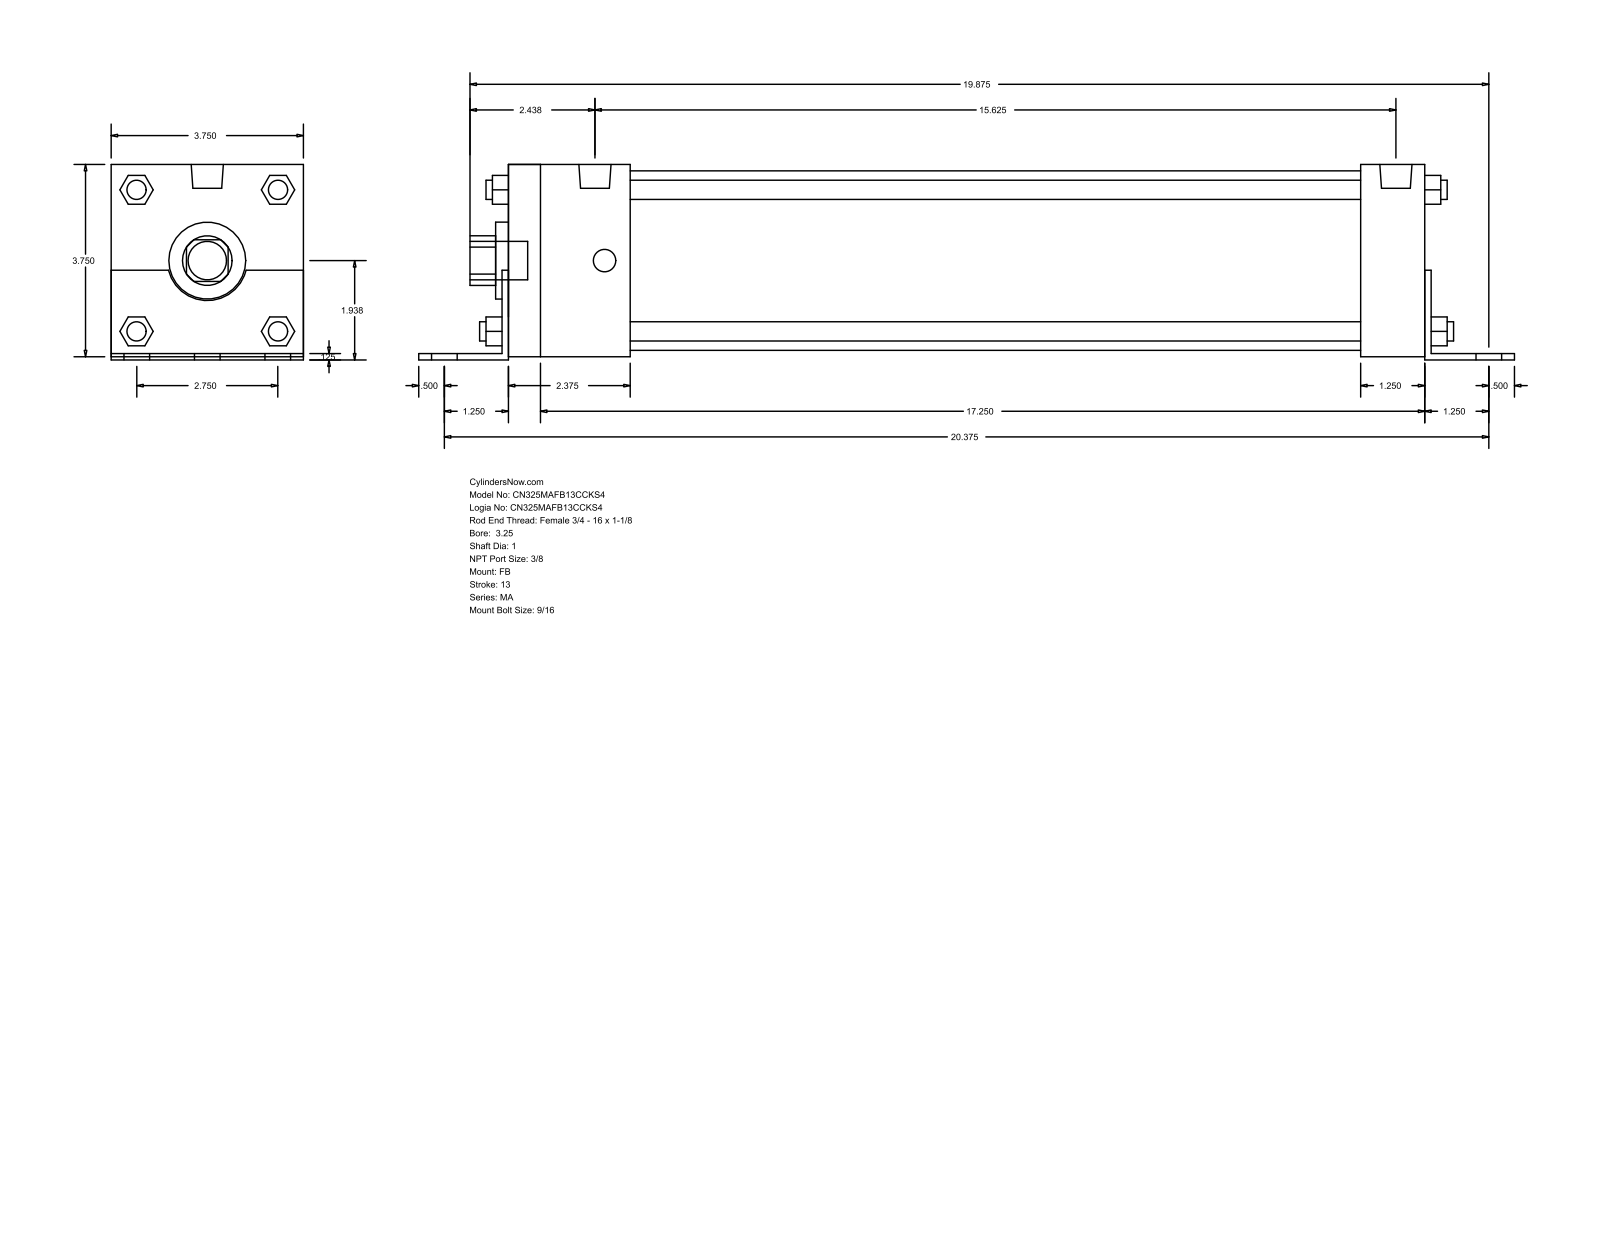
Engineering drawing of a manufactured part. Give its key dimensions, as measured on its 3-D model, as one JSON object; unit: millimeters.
{"part_name": "MA_FB__0325_1", "step_written_by": "GSSL Pune (CONFIG_CONTROL_DESIGN)", "units": "millimeters", "bodies": {"solids": 0, "faces": 140, "planar": 105, "cylindrical": 35, "other": 0}, "overall_size": [542.92, 96.84, 95.25], "round_holes": [[25.4, 1], [38.1, 1], [88.9, 1]], "round_bosses_or_shafts": [[14.29, 6], [11.11, 4], [9.53, 4], [15.93, 2], [19.05, 1]], "partial_cylinders_radius": [[12.29, 1], [19.81, 1]], "face_to_face_distances": [95.24, 3.17, 1.59, 96.83, 1.58, 93.66, 3.18, 454.02, 460.37, 457.2]}
